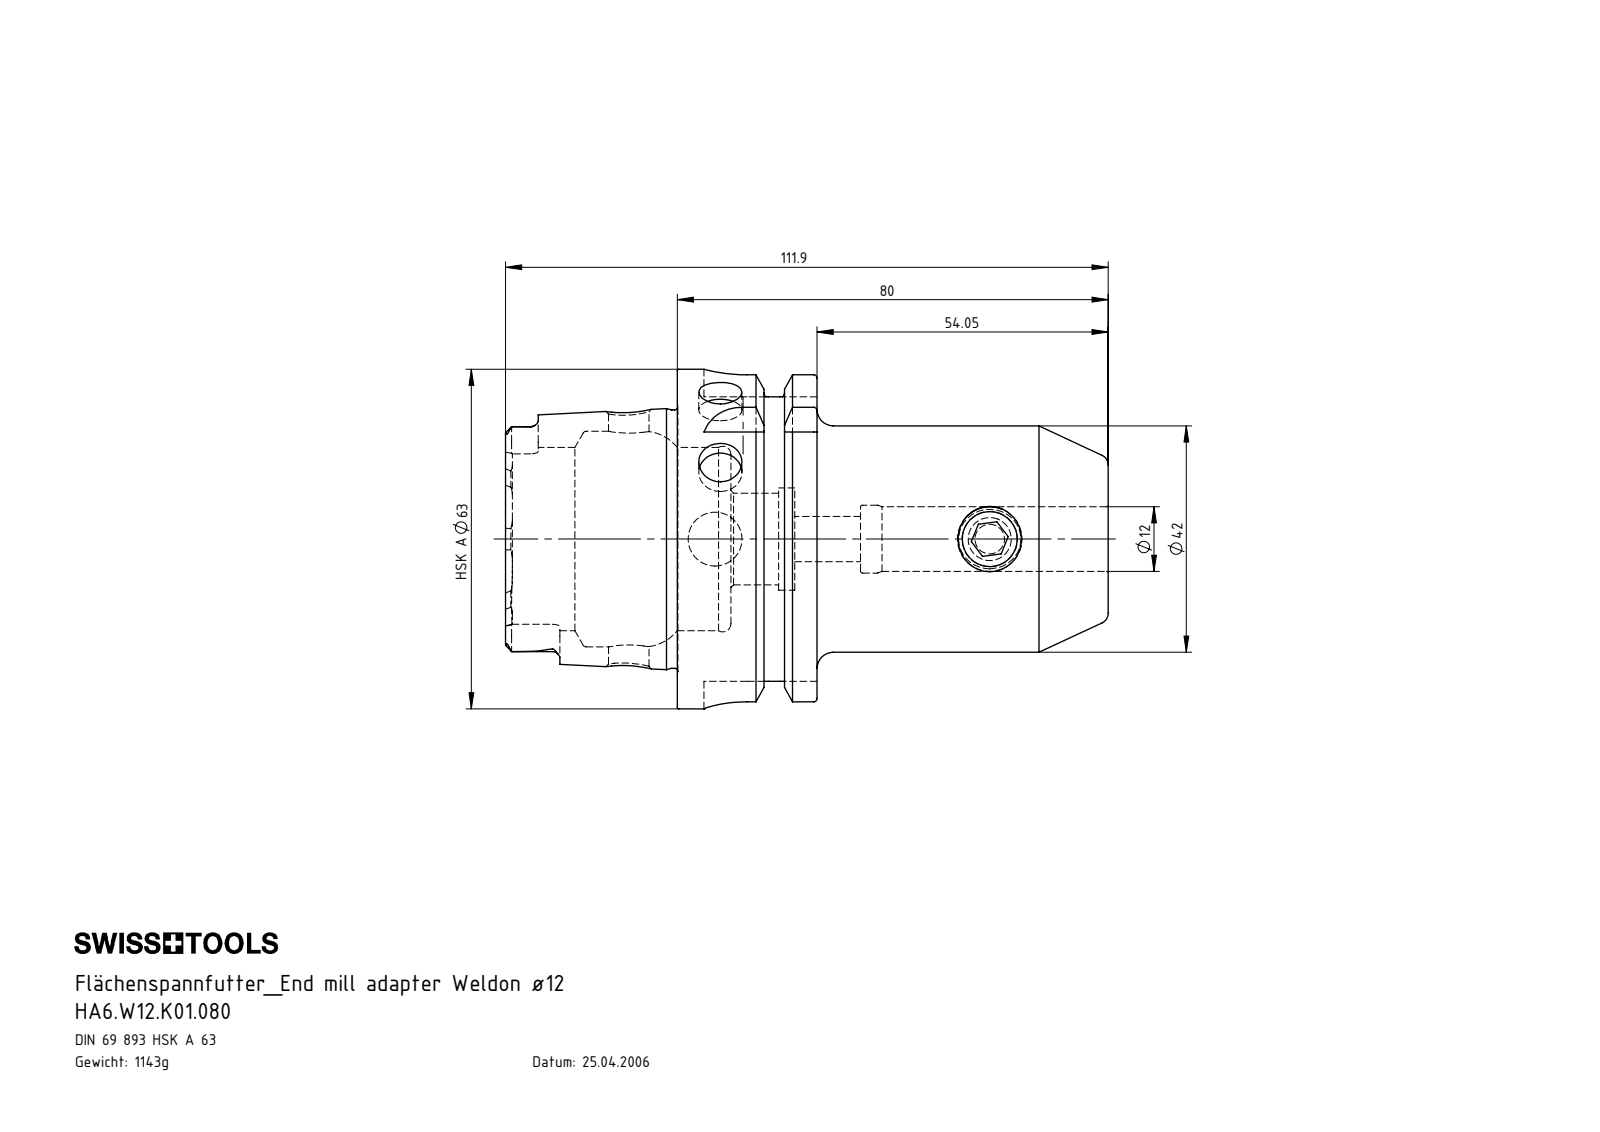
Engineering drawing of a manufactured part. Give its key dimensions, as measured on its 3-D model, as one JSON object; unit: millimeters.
{"part_name": "HA6.W12.K01.080; W12-ER1.001.016; HA6-W12.K01.080_B_Fertigbearbeitung", "step_written_by": "SolidWorks 2012 (CONFIG_CONTROL_DESIGN)", "units": "millimeters", "bodies": {"solids": 2, "faces": 208, "planar": 58, "cylindrical": 57, "other": 93}, "overall_size": [111.9, 63, 63], "volume_mm3": 145640, "surface_area_mm2": 31853, "round_holes": [[8, 2], [7.5, 1], [8.4, 1], [10, 1], [10.25, 1], [12, 1], [12.6, 1], [17, 1], [19, 1], [34, 1], [40, 1]], "round_bosses_or_shafts": [[63, 1], [54.95, 1], [47.94, 1], [42, 1], [12, 1]], "partial_cylinders_radius": [[1.4, 6], [2.88, 4], [8, 4]], "face_to_face_distances": [25.95, 16, 9.95, 80, 70.05, 54.05, 31.9, 41.85, 57.85, 111.9], "hole_center_spacings": [51]}
